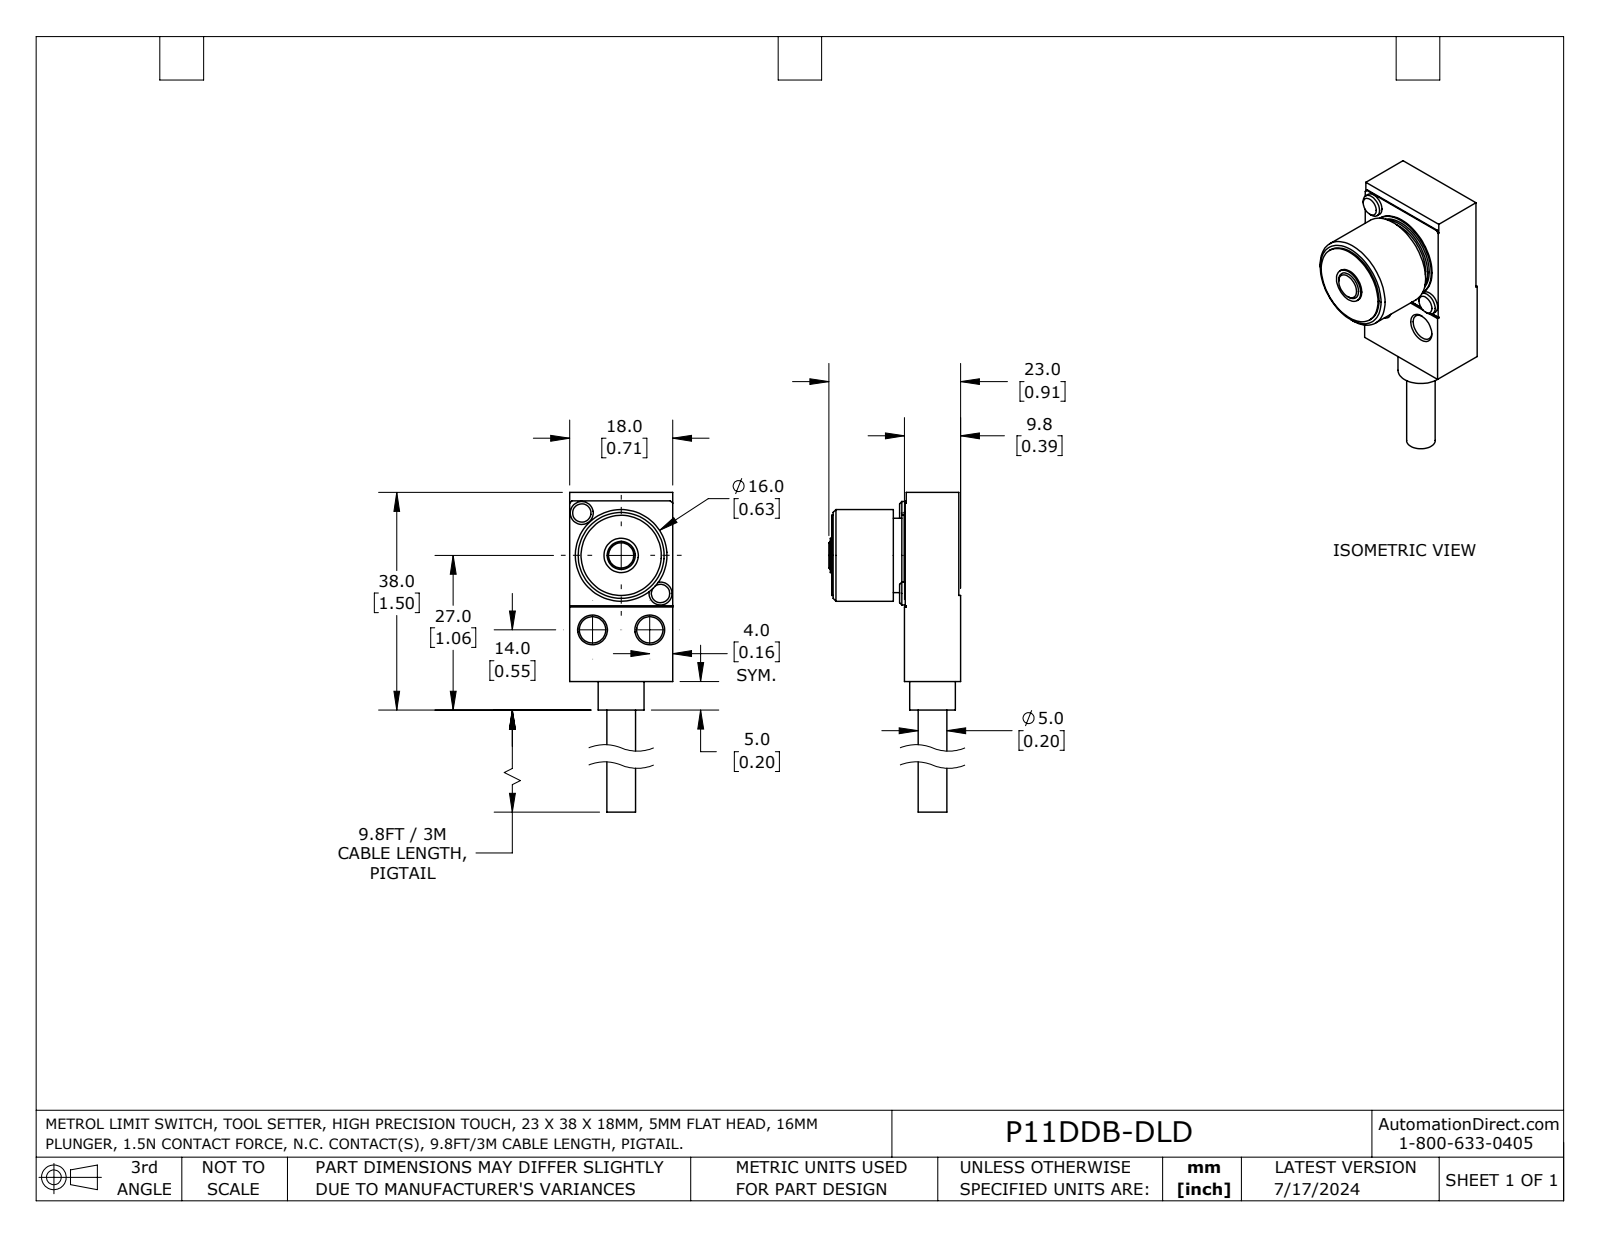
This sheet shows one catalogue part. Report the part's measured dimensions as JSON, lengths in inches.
{"part_name": "P11DDB-DLD", "step_written_by": "SolidWorks 2023 (AUTOMOTIVE_DESIGN)", "units": "inches", "bodies": {"solids": 1, "faces": 45, "planar": 27, "cylindrical": 12, "other": 6}, "overall_size": [2.087, 0.906, 0.709], "volume_in3": 0.51, "surface_area_in2": 5.461, "round_holes": [[0.181, 2]], "round_bosses_or_shafts": [[0.157, 2], [0.63, 1], [0.591, 1], [0.551, 1], [0.512, 1], [0.315, 1], [0.236, 1], [0.197, 1]], "face_to_face_distances": [0.709, 0.374, 0.386, 1.299, 0.38, 0.368, 0.886, 0.874, 0.506, 0.5], "hole_center_spacings": [0.394]}
